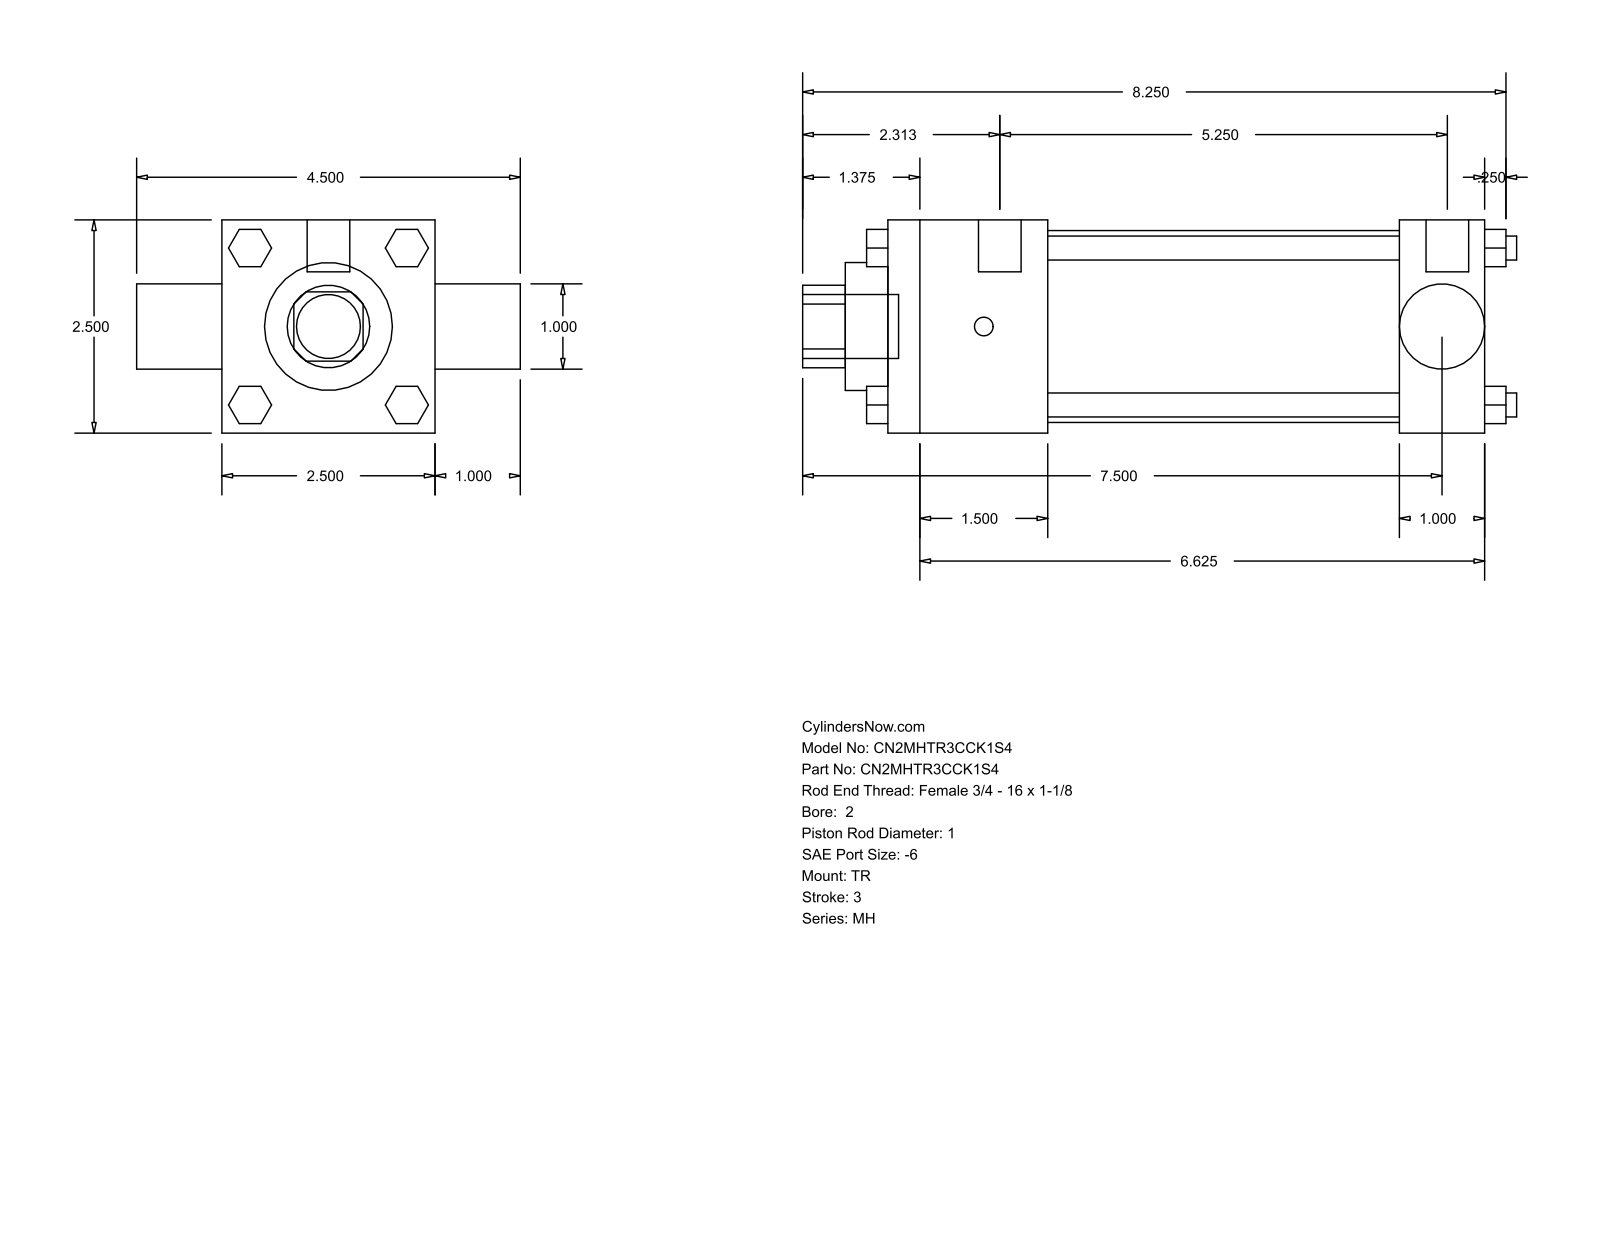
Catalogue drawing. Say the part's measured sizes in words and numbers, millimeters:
The part is named "MH_TR__0200_1". Its 3-D file was written by "GSSL Pune (CONFIG_CONTROL_DESIGN)". It is 0 solids with 120 faces: 92 planar, 28 cylindrical and 0 other. Overall it measures 212.72 by 114.3 by 63.5 millimeters. Round holes: 1 of diameter 25.35, 1 of diameter 25.4, 1 of diameter 38.1, 1 of diameter 57.15. Round bosses or shafts: 4 of diameter 7.14, 3 of diameter 5.56, 2 of diameter 12.7, 1 of diameter 19.05. Partial cylindrical surfaces (rounded edges, fillets, slot ends): 1 of radius 12.29. The main face-to-face distances are 63.5, 177.8, 25.4, 47.63, 152.4, 104.77, 130.17, 88.9, 190.5, 6.35.
